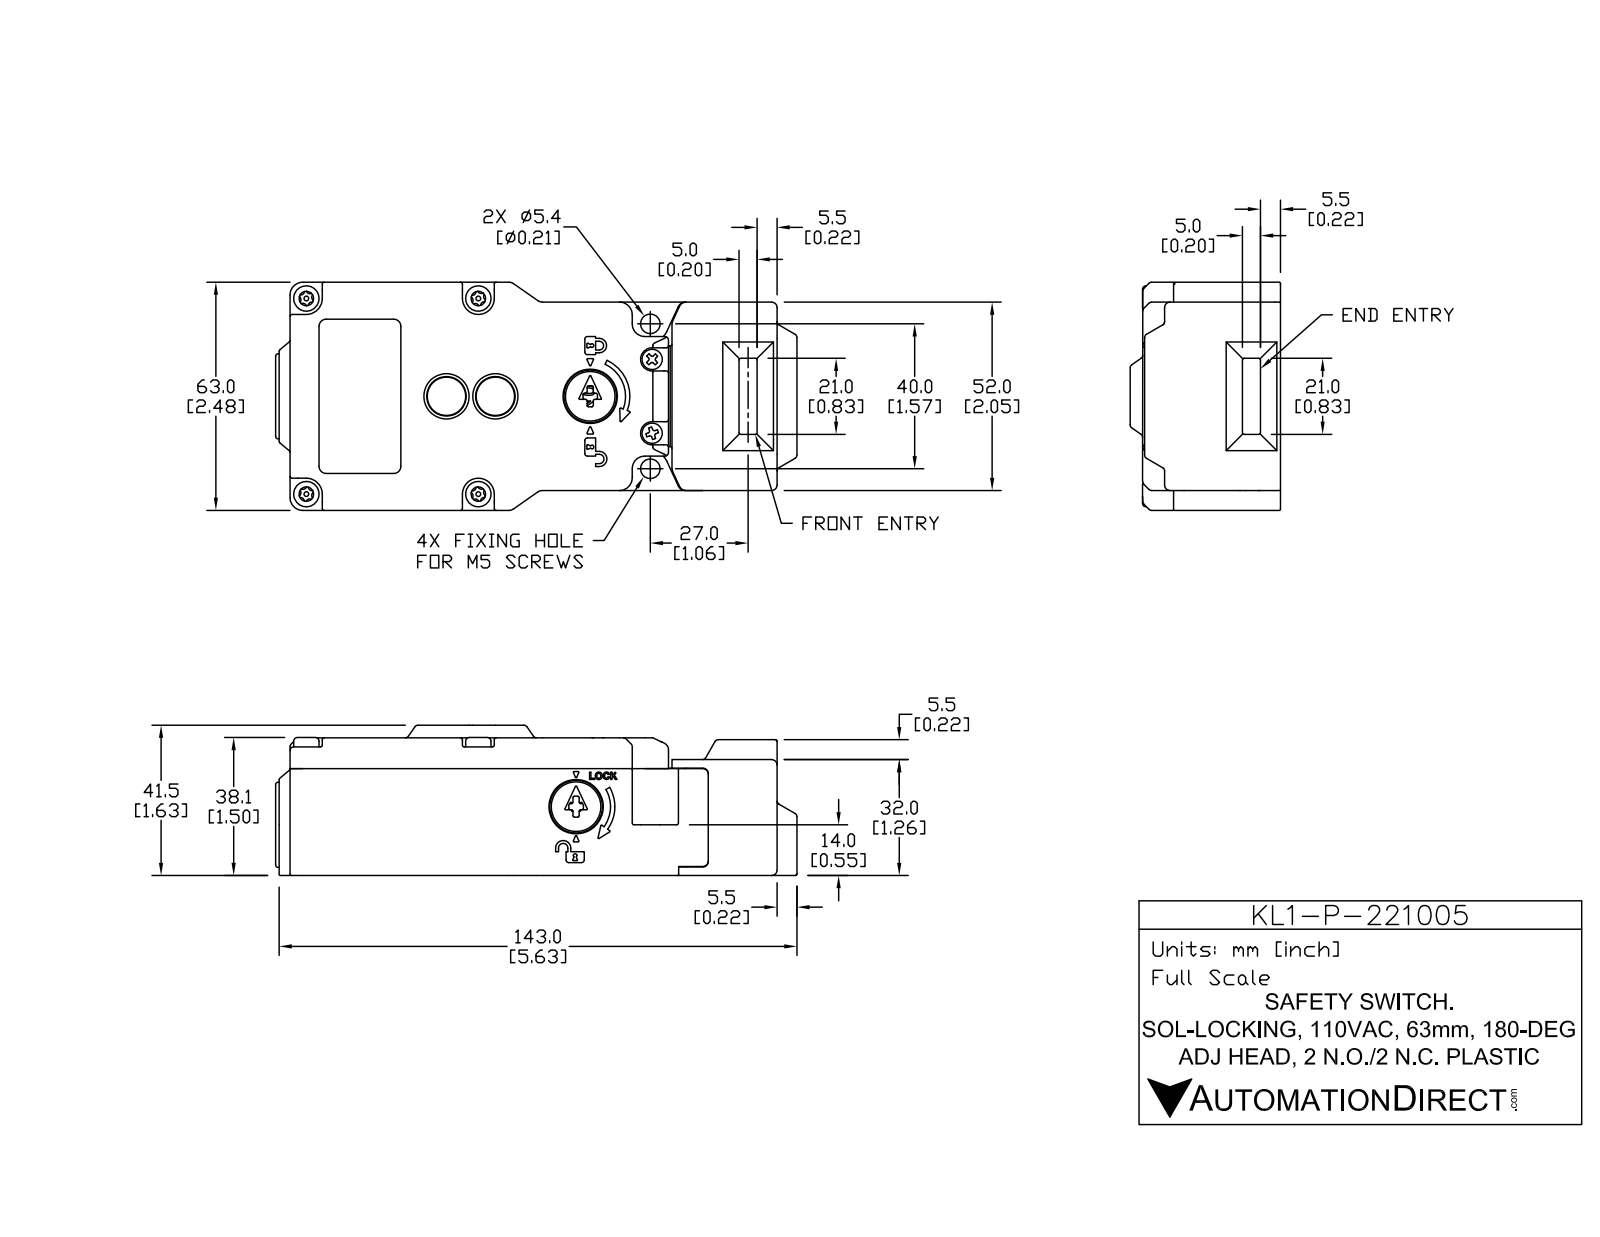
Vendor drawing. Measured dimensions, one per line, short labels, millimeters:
name: KL1-P-221005
written by: SolidWorks 2017 (AUTOMOTIVE_DESIGN)
unit: mm
bodies: 18 solids, 3047 faces (909 planar, 1225 cylindrical, 913 other)
size: 144 × 63 × 41.5
volume: 104 000 mm³; area: 76 650 mm²
holes: 4× ⌀2.6, 4× ⌀3.4, 4× ⌀4, 4× ⌀4.1, 4× ⌀4.5, 4× ⌀5, 2× ⌀2, 2× ⌀2.1, 2× ⌀3, 2× ⌀3.2, 2× ⌀3.6, 2× ⌀6.7
bosses: 4× ⌀7, 4× ⌀3.5, 4× ⌀1.3, 3× ⌀5, 3× ⌀1, 2× ⌀14.5, 2× ⌀10.6, 2× ⌀9.2
rounds: 348× R0.5, 126× R0.3, 106× R1, 30× R0.2, 24× R0.4, 16× R1.5, 14× R0.2, 12× R0.7
face distances: 2.5, 3, 5.5, 38, 35.5, 35.6, 33.1, 2.4, 57.5, 54.5
hole spacings: 10.3, 12.6, 13.1, 13.9, 19.9, 20.4, 27.4, 28.4
